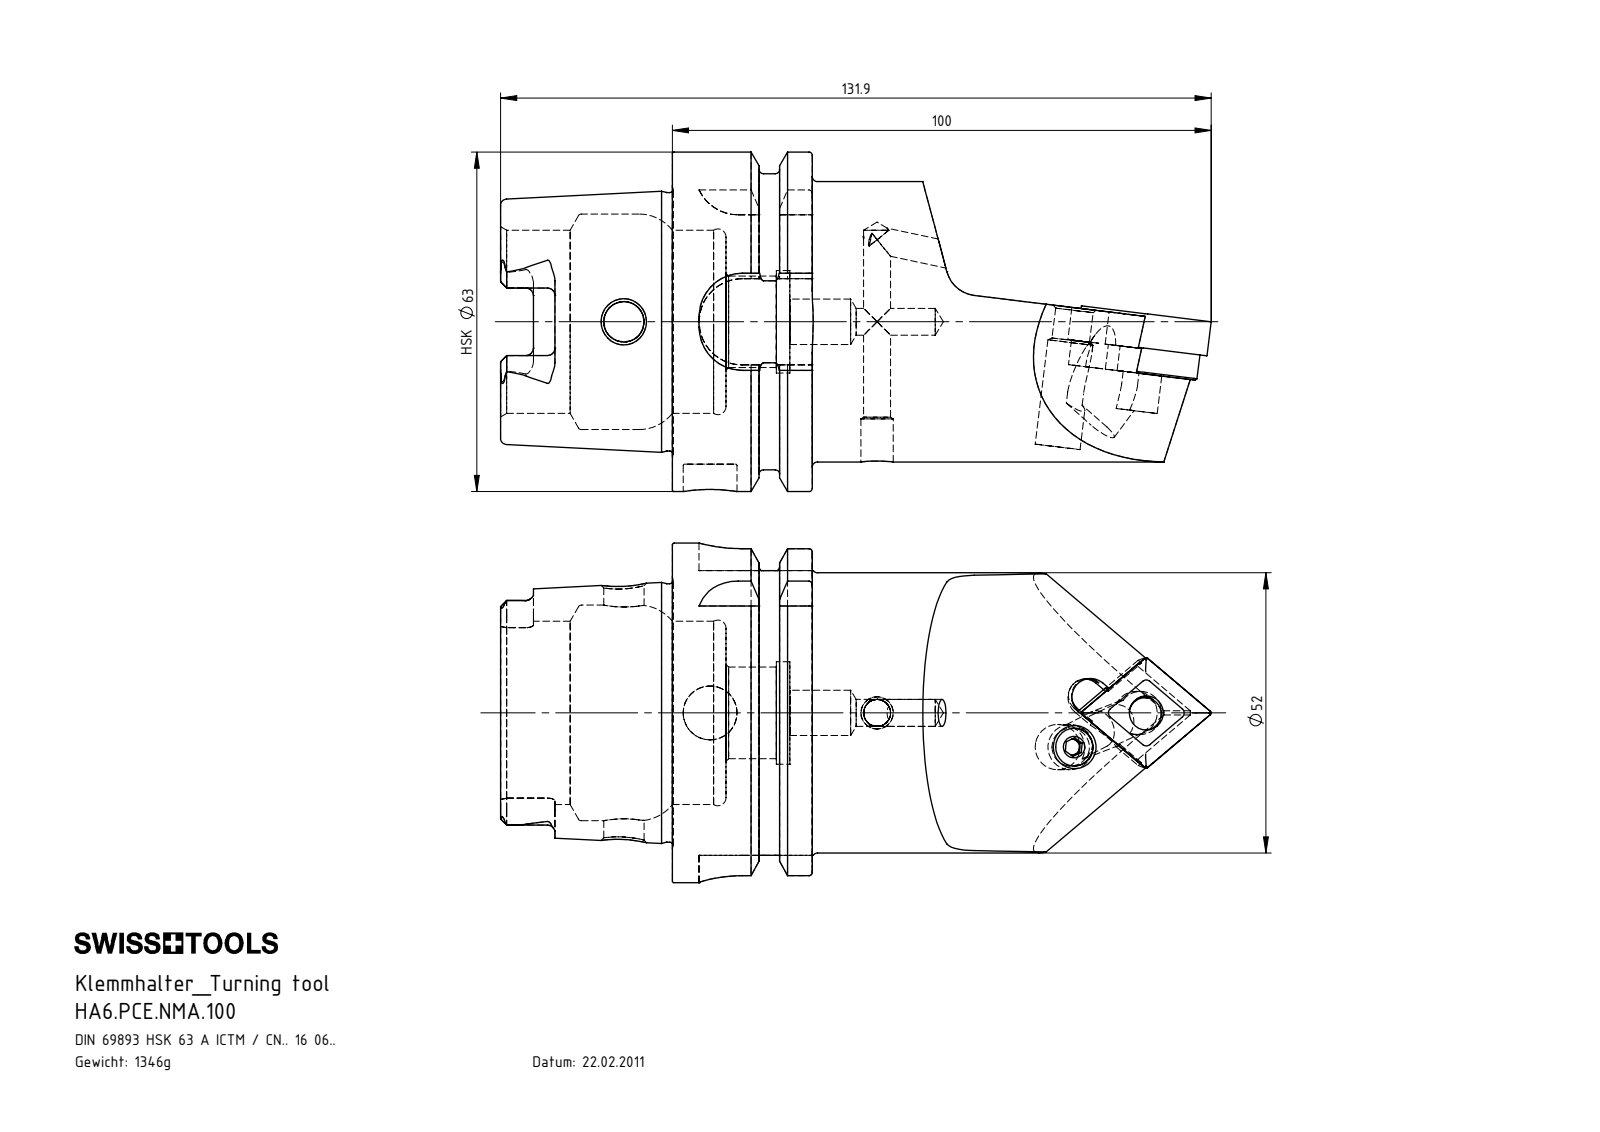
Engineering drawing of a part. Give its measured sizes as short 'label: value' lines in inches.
name: HA6.PCE.NMA.100; CNMG160604; WCE-ER2.101.004_A; WCE (+4 more)
written by: SolidWorks 2011 (CONFIG_CONTROL_DESIGN)
unit: in
bodies: 7 solids, 371 faces (119 planar, 104 cylindrical, 148 other)
size: 5.193 × 2.48 × 2.48
volume: 10.4 in³; area: 55.52 in²
holes: 3× ⌀0.197, 2× ⌀0.331, 1× ⌀0.25, 1× ⌀0.276, 1× ⌀0.295, 1× ⌀0.317, 1× ⌀0.394, 1× ⌀0.669, 1× ⌀0.748, 1× ⌀1.339, 1× ⌀1.575
bosses: 2× ⌀0.236, 1× ⌀2.48, 1× ⌀2.163, 1× ⌀2.047, 1× ⌀1.887, 1× ⌀0.315, 1× ⌀0.311, 1× ⌀0.252
rounds: 6× R0.055, 4× R0.016, 4× R0.059, 4× R0.315, 3× R0.138, 2× R0.111, 2× R0.113, 1× R0.122
face distances: 1.022, 0.63, 0.392, 0.23, 1.256, 1.648, 2.278, 2.079, 0.858, 0.467
hole spacings: 0.581, 0.591, 1.22
